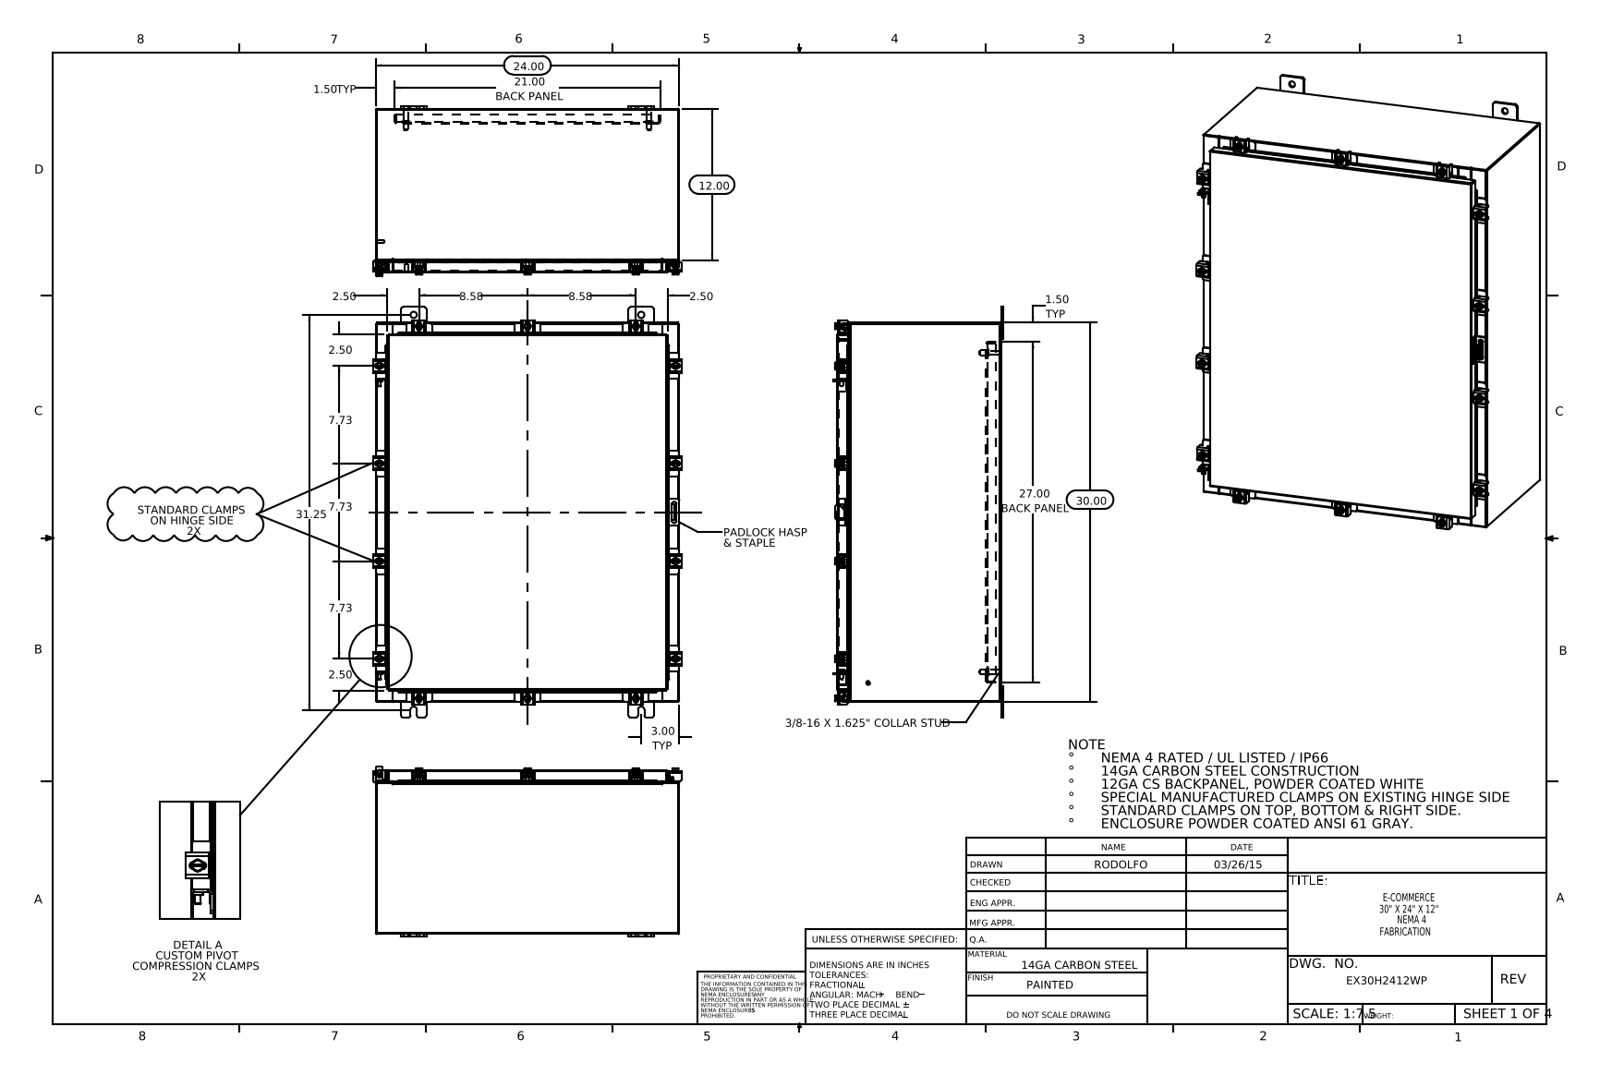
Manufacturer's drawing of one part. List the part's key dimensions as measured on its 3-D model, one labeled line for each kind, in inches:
Part name (STEP PRODUCT): EX30H2412WP Bottom; Special Clamp Assembly; 22101002_RTP29; EX30H2412WP Top (+8 more)
STEP written by: SolidWorks 2014 (CONFIG_CONTROL_DESIGN)
Units: inches
Bodies: 91 solids, 2272 faces (1211 planar, 885 cylindrical, 176 other)
Overall size (bounding box): 32.5 × 24.421 × 13.453
Volume: 296.7 in³ · Surface area: 7 434 in²
Round holes (diameter × count): ⌀0.213 ×14, ⌀0.26 ×14, ⌀0.5 ×8, ⌀0.125 ×1, ⌀0.25 ×1
Round bosses / shafts (diameter × count): ⌀0.5 ×14, ⌀0.25 ×14, ⌀0.399 ×12, ⌀0.625 ×4, ⌀0.375 ×4, ⌀0.33 ×4, ⌀0.315 ×2, ⌀0.236 ×2
Partial cylindrical surfaces — rounded edges, fillets, slot ends (radius × count): R0.06 ×62, R0.141 ×28, R0.013 ×26, R0.12 ×26, R0.19 ×24, R0.088 ×22, R0.09 ×20, R0.05 ×19
Main face-to-face distances: 0.075, 12.9, 23.925, 12.975, 12.826, 0.104, 1, 29.925, 1.075, 11.826
Hole centre spacings: 2.347, 4.44, 20.544, 23.451, 24.31, 26.507, 27.37, 32.286
